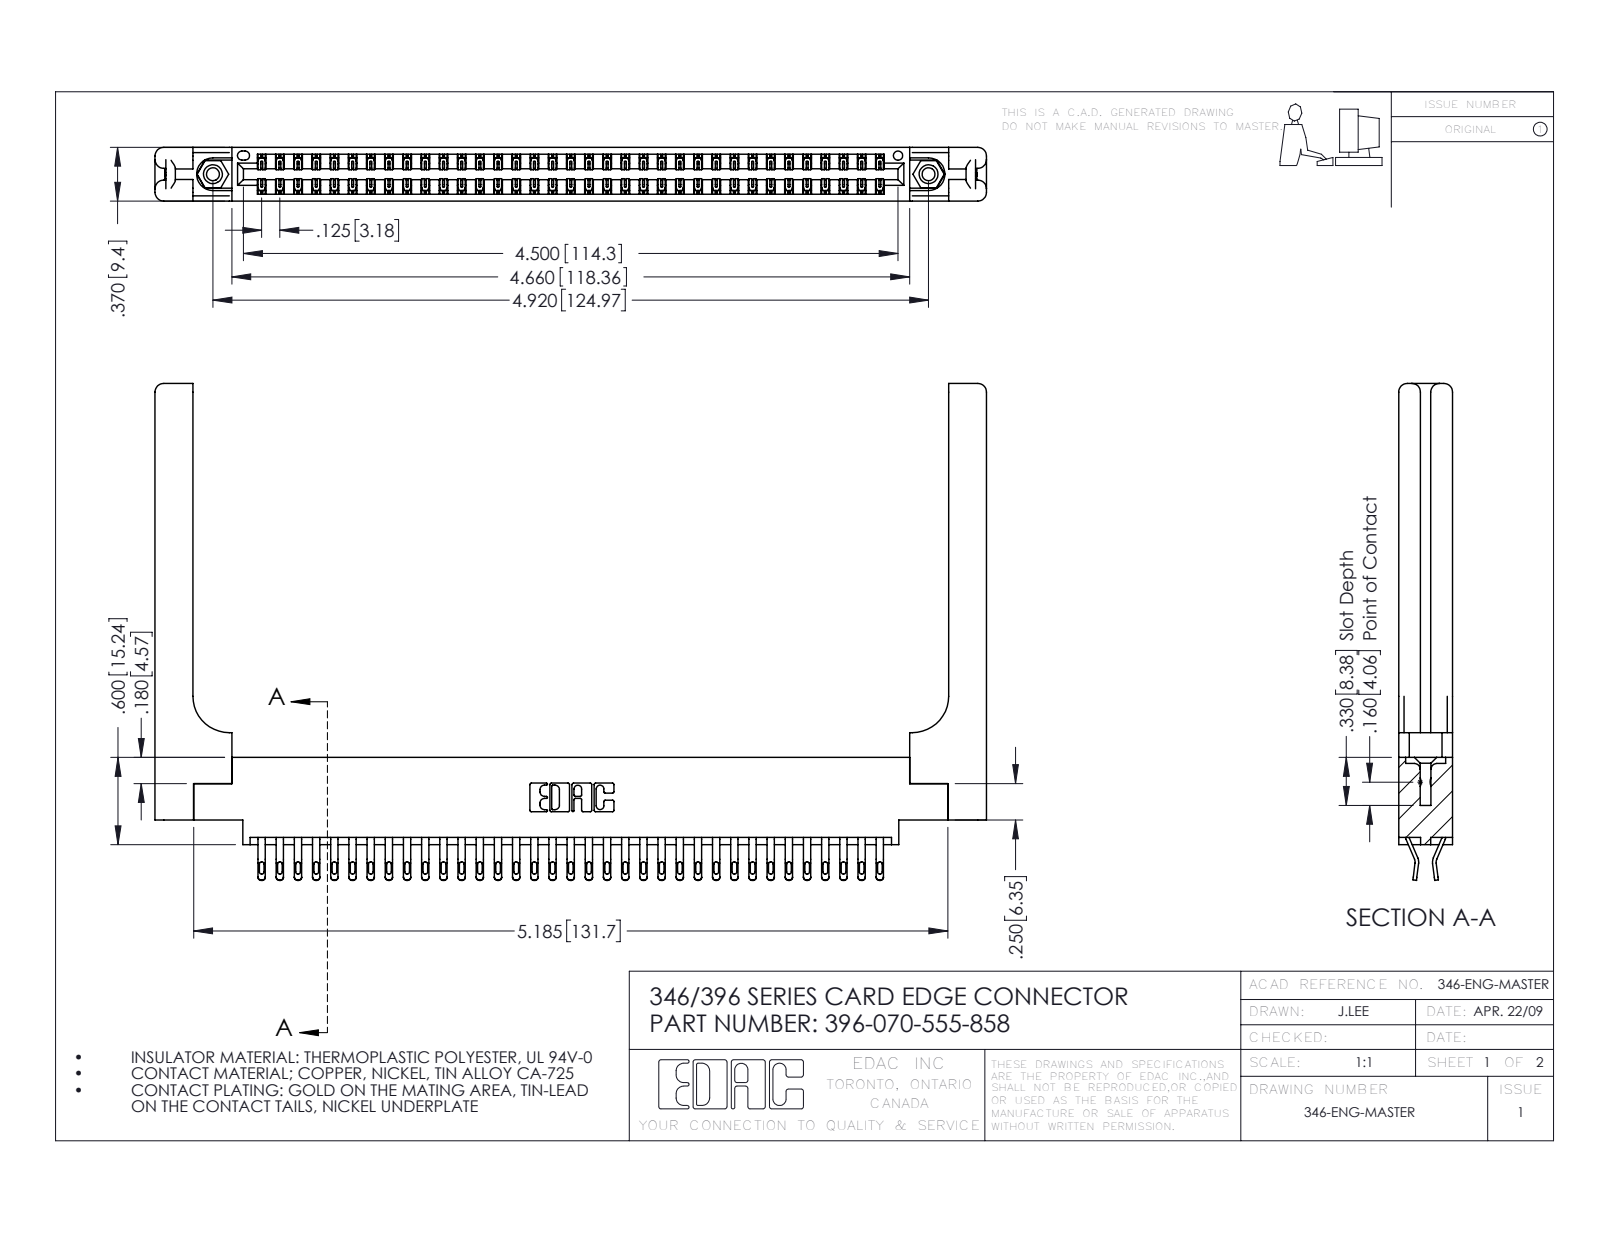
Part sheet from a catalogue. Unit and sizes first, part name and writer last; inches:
Units: inches
Overall size (bounding box): 5.716 × 3.415 × 0.37
Round holes (diameter × count): ⌀0.089 ×2, ⌀0.125 ×2, ⌀0.156 ×2, ⌀0.064 ×1
Round bosses / shafts (diameter × count): ⌀0.155 ×2
Partial cylindrical surfaces — rounded edges, fillets, slot ends (radius × count): R0.016 ×140, R0.02 ×140, R0.006 ×105, R0.01 ×22, R0.06 ×16, R0.007 ×6, R0.031 ×6, R0.026 ×3
Main face-to-face distances: 0.37, 0.048, 0.322, 0.072, 0.148, 0.15, 0.25, 0.025, 0.298, 0.275
Hole centre spacings: 0.246, 4.711, 4.92
Volume: 1.321 in³ · Surface area: 39.09 in²
Bodies: 75 solids, 4442 faces (2538 planar, 1844 cylindrical, 60 other)
Part name (STEP PRODUCT): 346 Part_0.170 Offset - 0.156 Dia-TH; 345-292-001_555 Tail; 346-220-058_345-220-058; 396-070-555-858 (+1 more)
STEP written by: SolidWorks 2016 (CONFIG_CONTROL_DESIGN)
